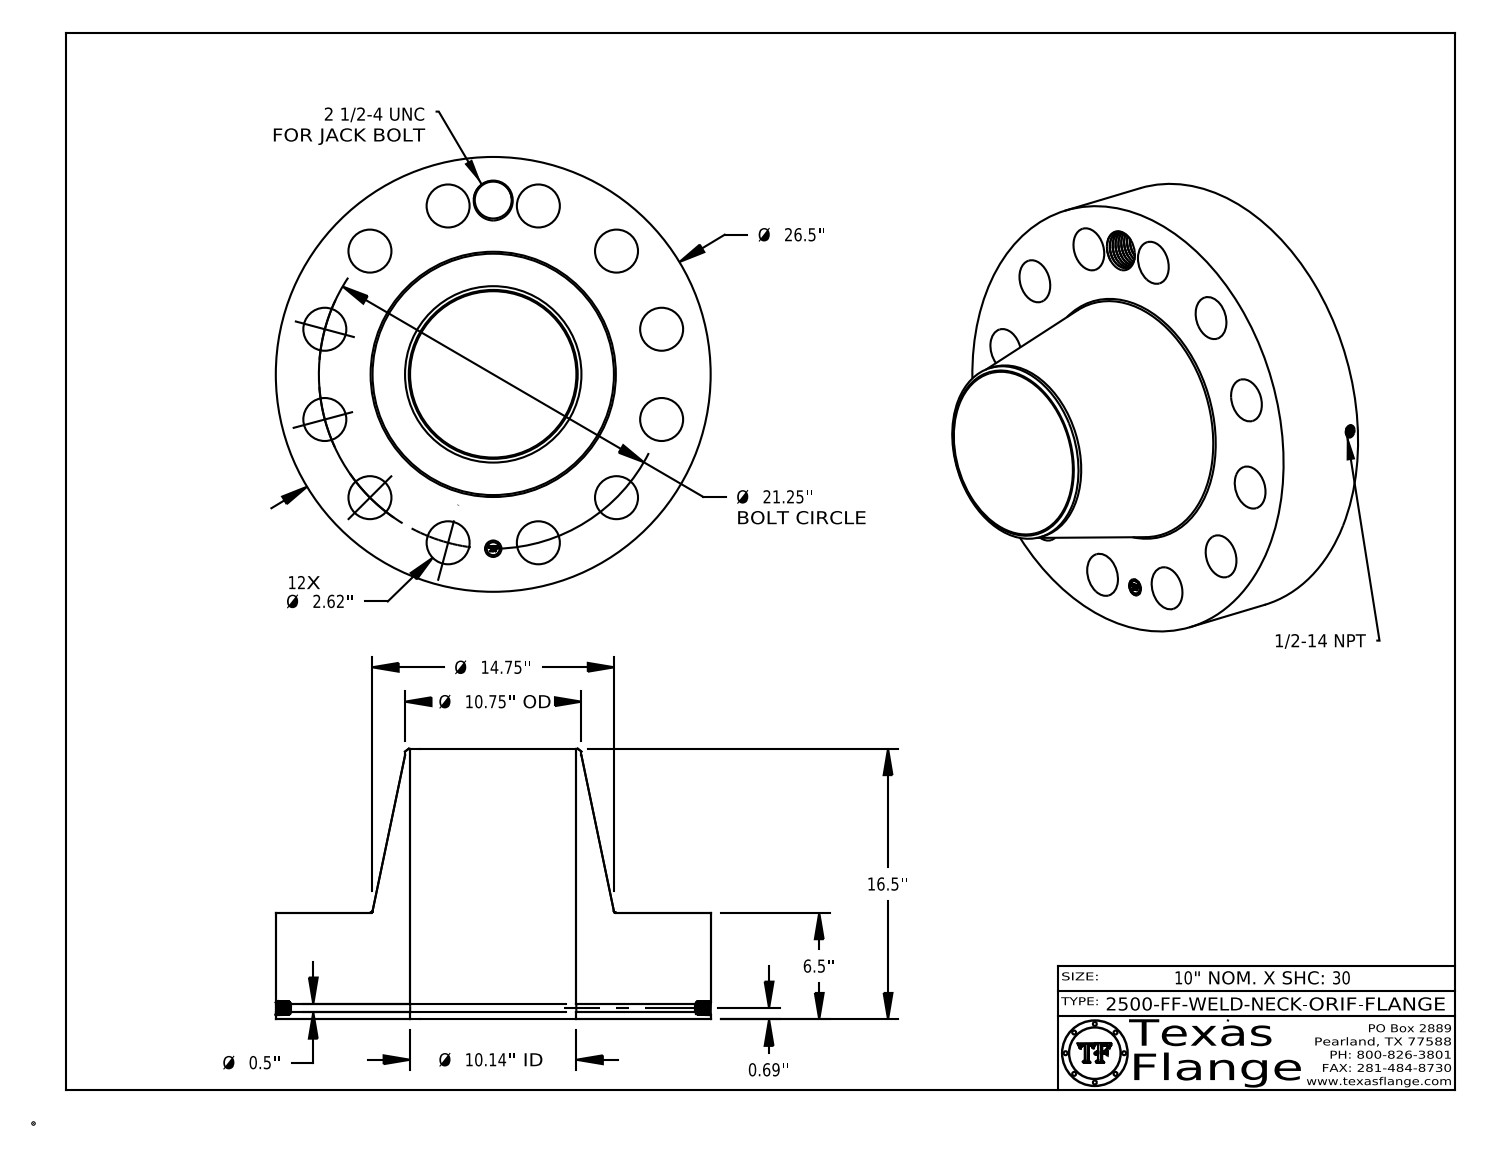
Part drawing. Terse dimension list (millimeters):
name: 2500-FF-WELD-NECK
written by: CATIA V5 STEP AP214 (AUTOMOTIVE_DESIGN)
unit: mm
bodies: 1 solid, 840 faces (368 planar, 122 cylindrical, 350 other)
size: 673.1 × 673.1 × 419.1
volume: 50 340 000 mm³; area: 1 891 000 mm²
holes: 12× ⌀66.5, 1× ⌀12.7, 1× ⌀17.1, 1× ⌀25.4, 1× ⌀57.2, 1× ⌀257.5
bosses: 8× ⌀1.5, 1× ⌀673.1, 1× ⌀273.1, 1× ⌀20
face distances: 165.1, 419.1, 254, 0.4, 164.7, 254.4, 7.6, 7.4, 1.4, 6.3
hole spacings: 269.9, 139.7, 381.7, 467.4, 521.4, 269.9, 539.8, 70.5
